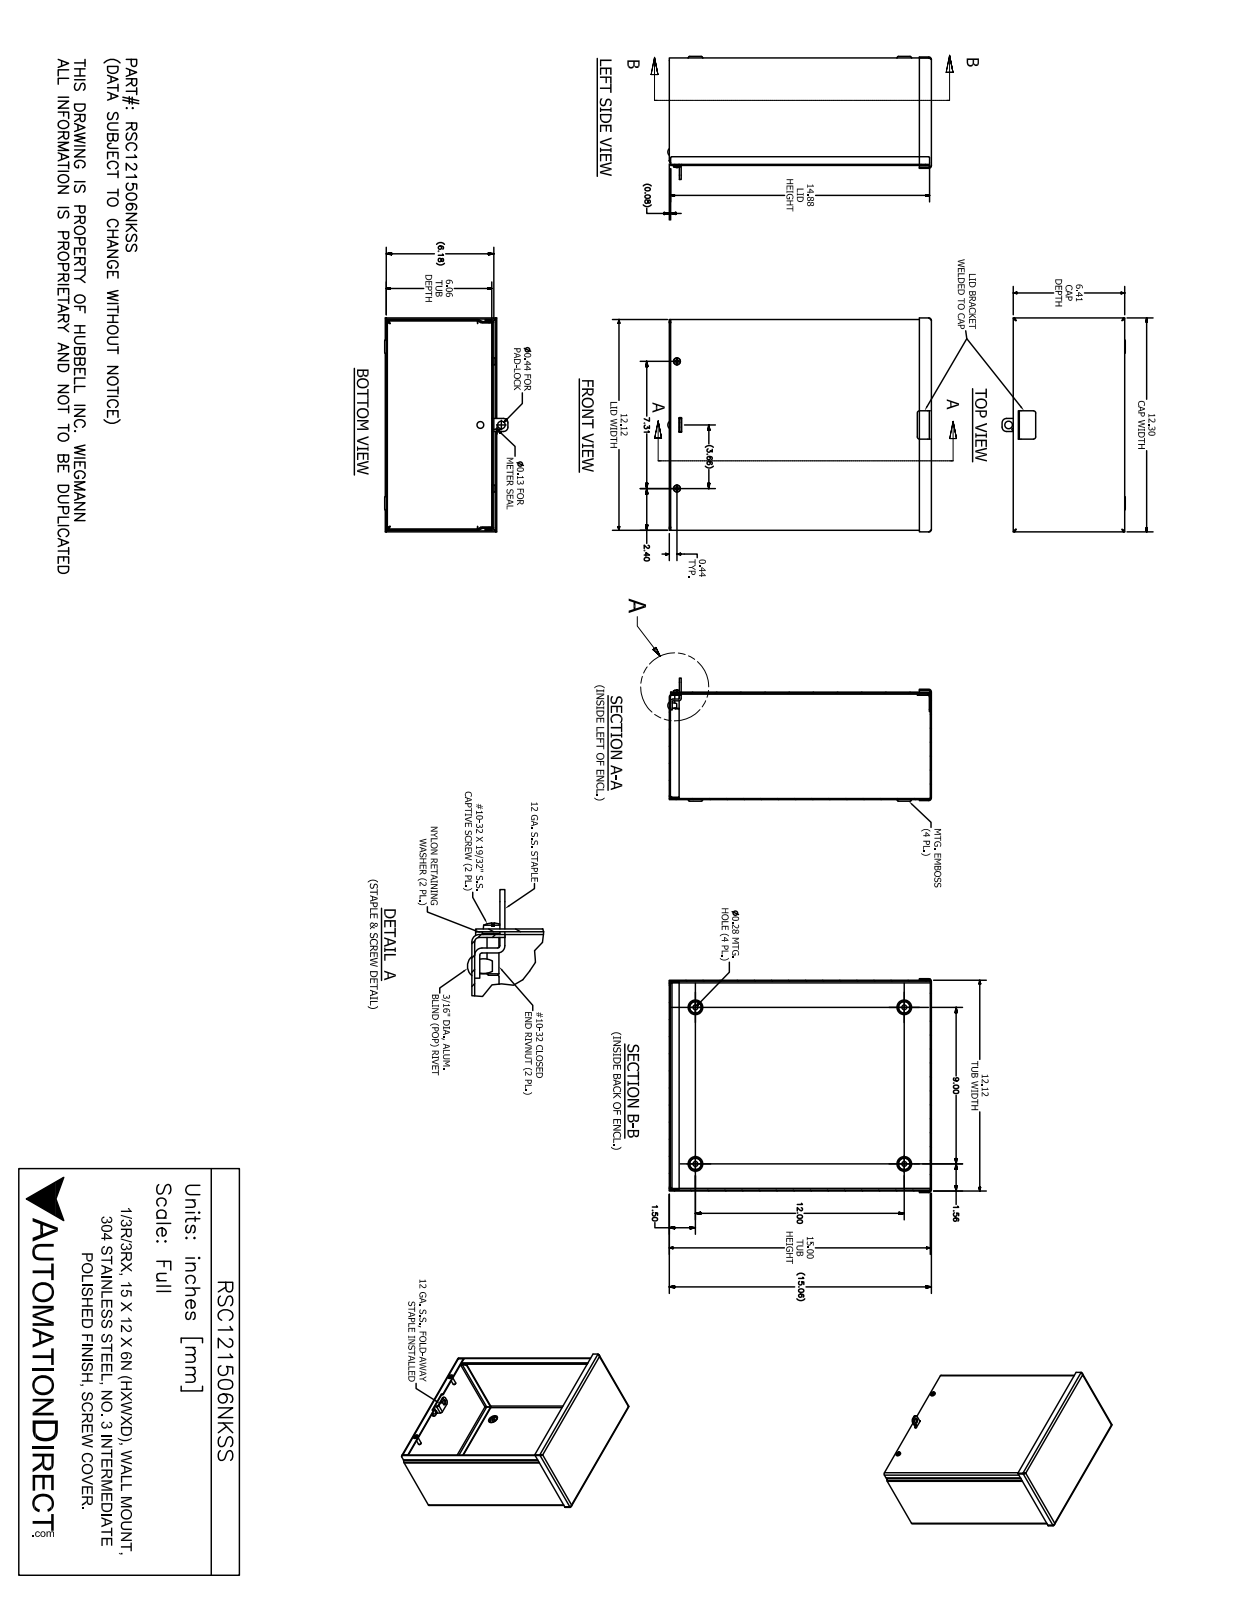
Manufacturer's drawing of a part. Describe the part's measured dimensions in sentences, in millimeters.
The part is named "RSC121506NKSS". Its 3-D file was written by "SolidWorks 2017 (AUTOMOTIVE_DESIGN)". It is 13 solids with 383 faces: 199 planar, 99 cylindrical and 85 other. Overall it measures 384.8 by 312.4 by 179.9 millimeters. Its volume is 723 500 cubic millimeters and its surface area 974 200 square millimeters. Round holes: 4 of diameter 6.4, 4 of diameter 7.1, 2 of diameter 4, 2 of diameter 5, 2 of diameter 6.5, 2 of diameter 7.1, 1 of diameter 3.2, 1 of diameter 5, 1 of diameter 5.1, 1 of diameter 11.1. Round bosses or shafts: 2 of diameter 11.5, 2 of diameter 10.3, 2 of diameter 6.3, 2 of diameter 4.2, 1 of diameter 4.7. Partial cylindrical surfaces (rounded edges, fillets, slot ends): 17 of radius 2.4, 17 of radius 3.9, 6 of radius 0.8, 4 of radius 3.2, 4 of radius 6.4, 2 of radius 1.2, 2 of radius 1.3, 2 of radius 1.6. The main face-to-face distances are 1.5, 155.4, 156.9, 153.9, 306.3, 381, 307.8, 304.8, 379.5, 382.5. The hole center spacings are 34.5, 35.1, 185.8, 208.9, 209, 228.6, 304.8, 332.5.
